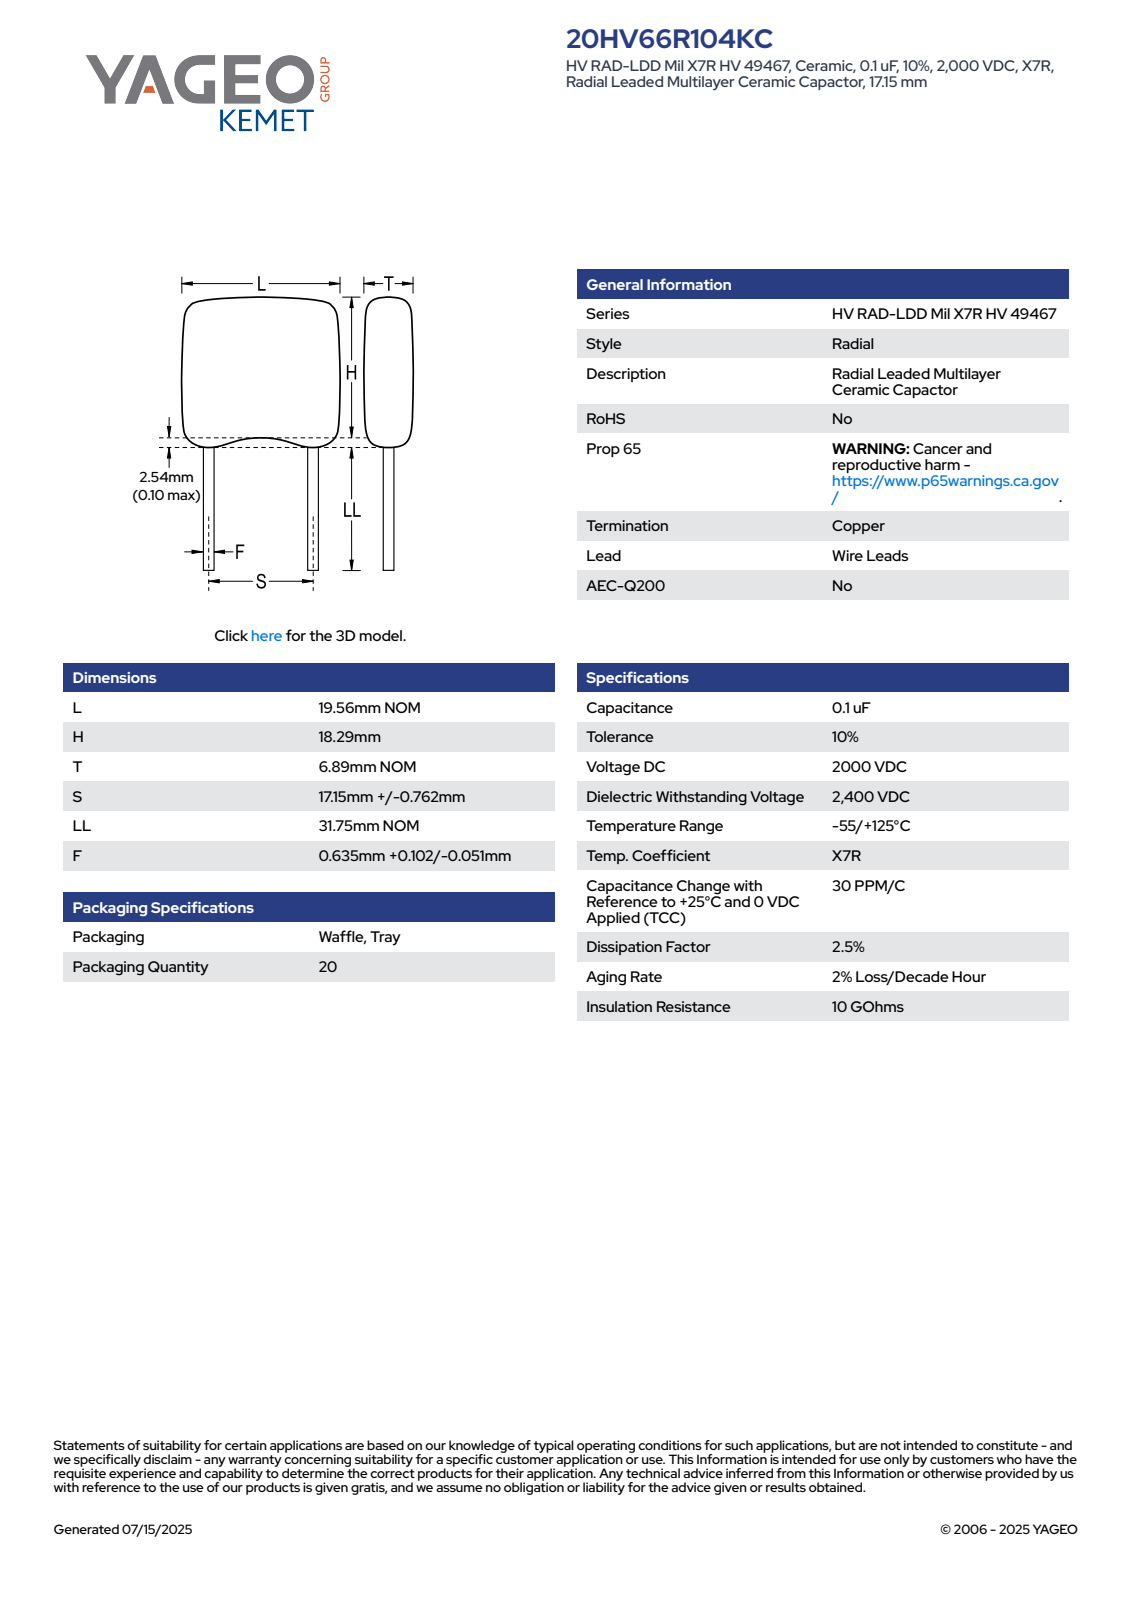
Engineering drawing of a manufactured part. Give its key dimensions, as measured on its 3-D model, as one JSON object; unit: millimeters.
{"part_name": "CCRM_RCST_HV66_L19.56H18.29T6.89S17.15LL31.75F0.737", "step_written_by": "SolidWorks 2021 (AUTOMOTIVE_DESIGN)", "units": "millimeters", "bodies": {"solids": 4, "faces": 98, "planar": 66, "cylindrical": 20, "other": 12}, "overall_size": [23.05, 19.56, 6.89], "volume_mm3": 2516, "surface_area_mm2": 1275, "round_bosses_or_shafts": [[0.74, 2]], "partial_cylinders_radius": [[1, 8], [0.5, 4]], "face_to_face_distances": [6.89, 19.56, 19.87, 3.17, 23.04, 14.46, 11.29, 8.58, 11.97, 8.8]}
